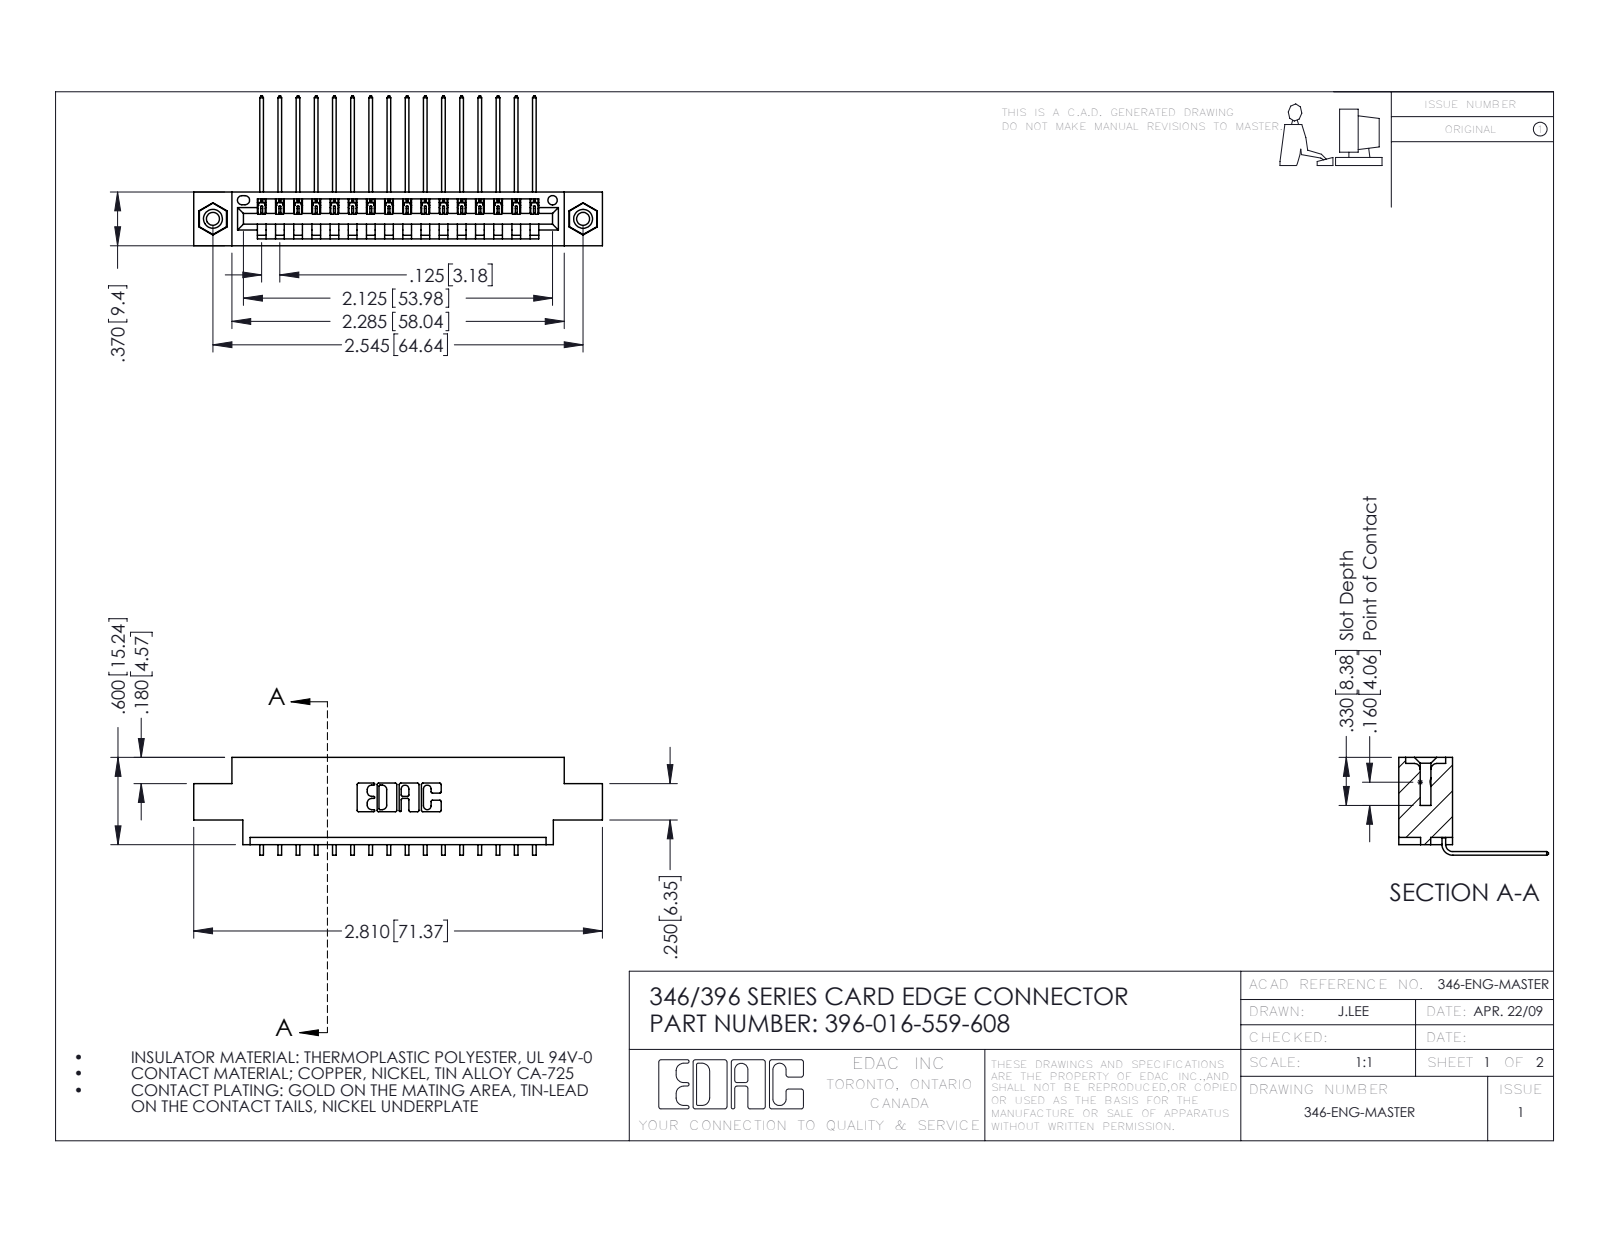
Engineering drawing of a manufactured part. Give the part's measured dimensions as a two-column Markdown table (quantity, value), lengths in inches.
| quantity | value |
| --- | --- |
| part name | 345-250-001_345-250-003-102; 396-016-559-608; 345-292-001_558 559 Tail - 1; 346 Part_0.170 Offset - 0.156 Dia-TI |
| STEP written by | SolidWorks 2016 (CONFIG_CONTROL_DESIGN) |
| units | inches |
| bodies | 19 solids, 1146 faces (784 planar, 346 cylindrical, 16 other) |
| overall size | 2.81 × 1.03 × 0.673 |
| volume | 0.399 in³ |
| surface area | 13.02 in² |
| round holes (diameter × count) | 0.089 × 2, 0.125 × 2, 0.156 × 2, 0.064 × 1 |
| round bosses / shafts (diameter × count) | 0.155 × 2 |
| partial cylindrical surfaces (radius × count) | 0.006 × 32, 0.01 × 22, 0.007 × 6, 0.031 × 6, 0.026 × 3, 0.031 × 2, 0.04 × 2, 0.014 × 1 |
| main face-to-face distances | 0.048, 0.37, 0.322, 0.25, 0.025, 0.072, 0.222, 0.148, 0.1, 0.174 |
| hole center spacings | 0.246, 2.338, 2.545 |
